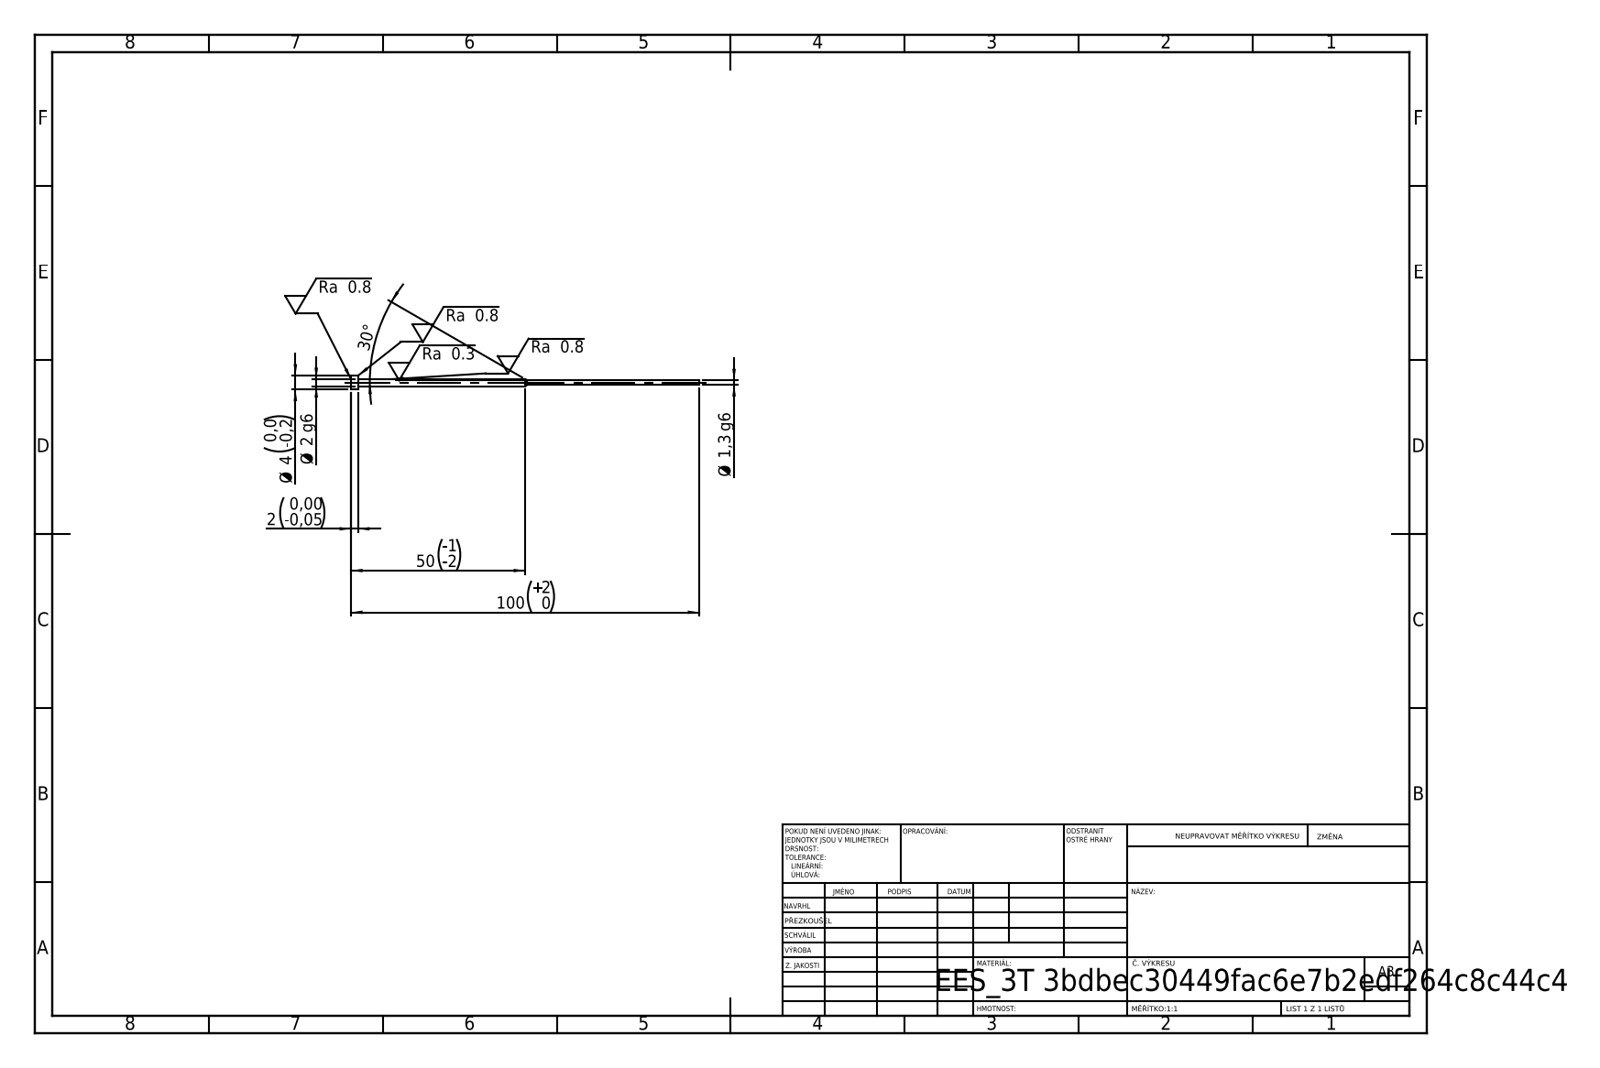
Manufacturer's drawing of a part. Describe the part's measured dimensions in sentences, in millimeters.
Its 3-D file was written by "SolidWorks 2019 (CONFIG_CONTROL_DESIGN)". It is 1 solid with 11 faces: 3 planar, 6 cylindrical and 2 other. Overall it measures 100 by 4 by 4 millimeters. Its volume is 243 cubic millimeters and its surface area 555 square millimeters. Round bosses or shafts: 1 of diameter 4, 1 of diameter 2, 1 of diameter 1.3. The main face-to-face distances are 2, 98, 100.
